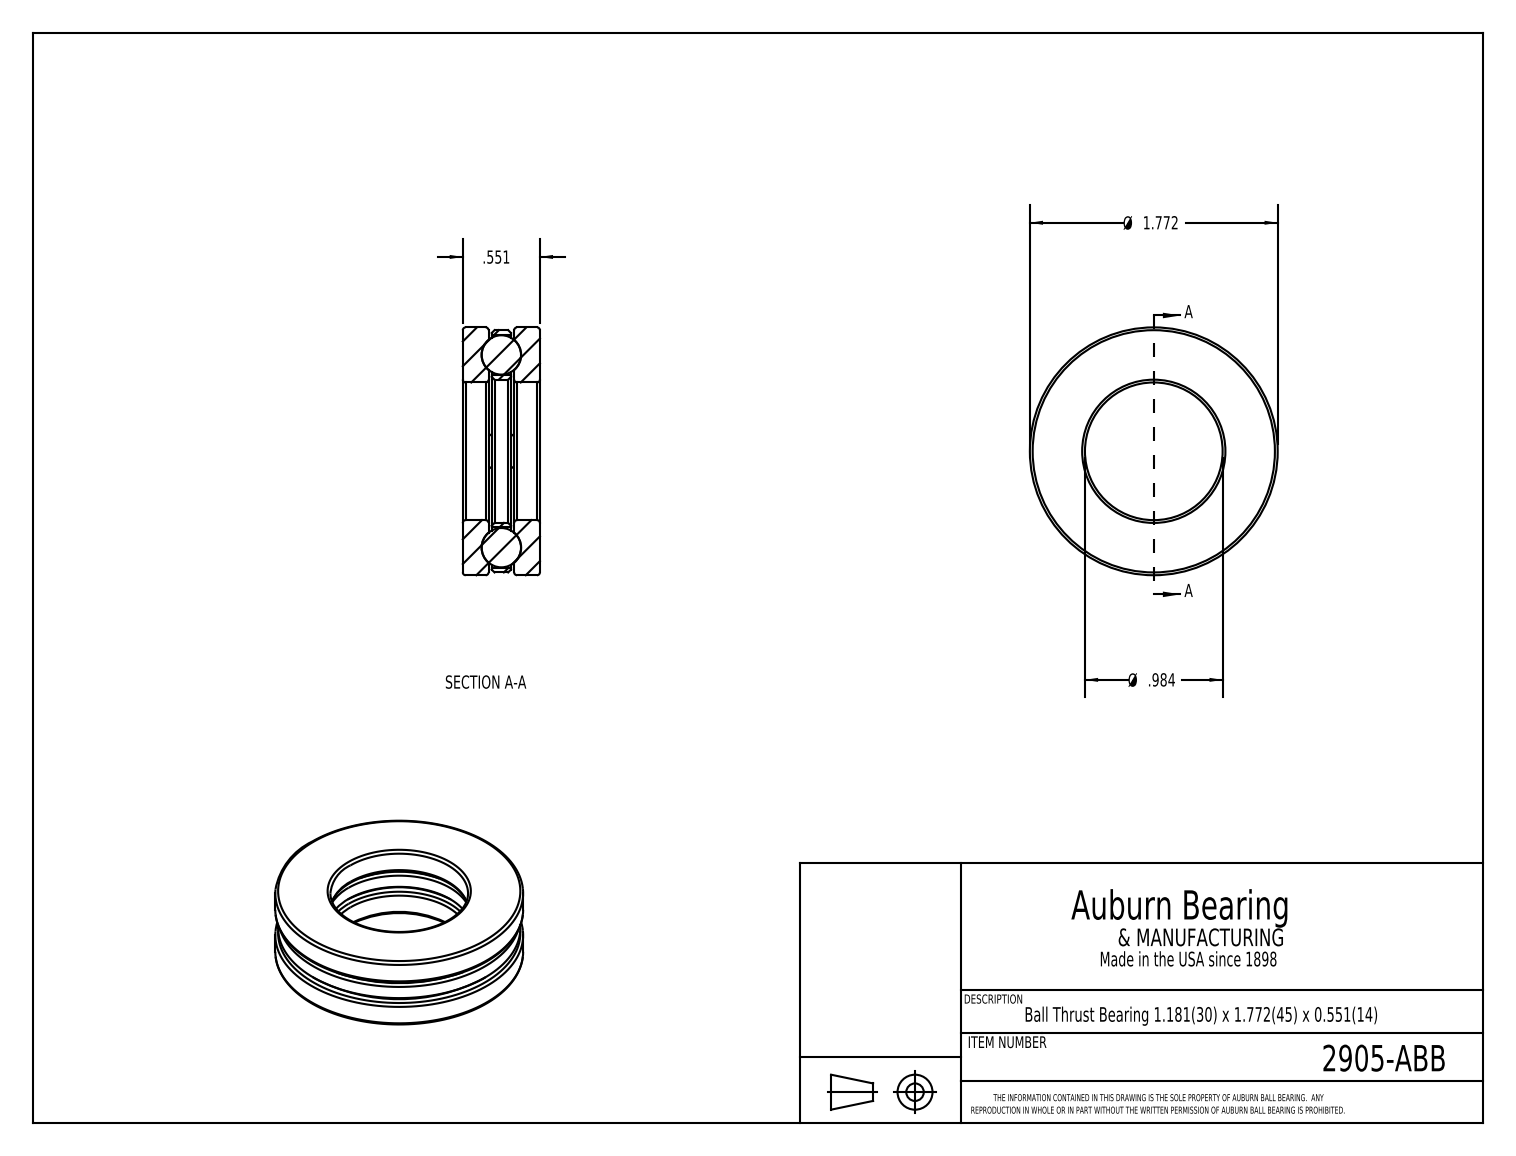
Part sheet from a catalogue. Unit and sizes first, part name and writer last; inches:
Units: inches
Overall size (bounding box): 1.772 × 1.772 × 0.551
Round holes (diameter × count): ⌀0.291 ×4, ⌀0.138 ×2, ⌀0.184 ×2, ⌀1.181 ×1, ⌀1.221 ×1
Round bosses / shafts (diameter × count): ⌀0.551 ×2, ⌀1.772 ×1, ⌀1.732 ×1
Main face-to-face distances: 0.367, 0.184, 0.551, 0.207, 0.344, 0.161, 0.295, 1.476, 0.023, 1.772
Hole centre spacings: 0.738, 1.044, 1.476
Volume: 0.85 in³ · Surface area: 17.33 in²
Bodies: 7 solids, 127 faces (39 planar, 36 cylindrical, 52 other)
Part name (STEP PRODUCT): 2905-ABB
STEP written by: SolidWorks 2017 (CONFIG_CONTROL_DESIGN)
